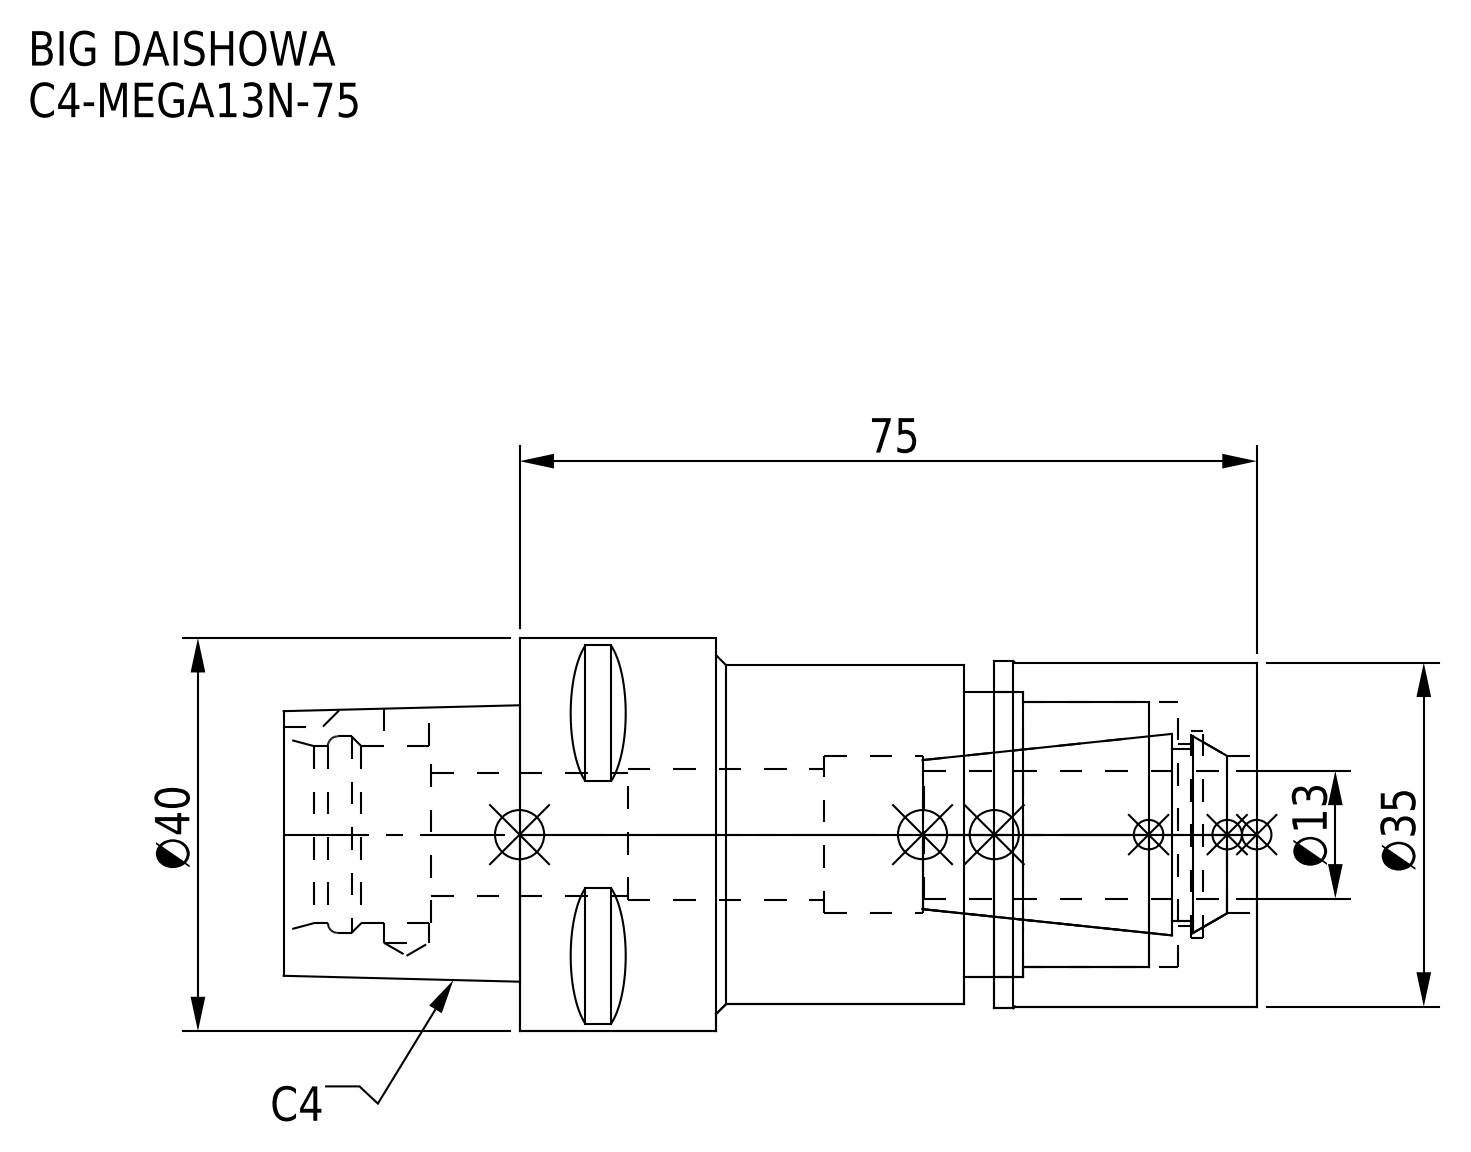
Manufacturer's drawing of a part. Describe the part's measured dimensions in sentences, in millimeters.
The part is named "C4-MEGA13N-75; MGN13_1.stp; C4-MEGA13N-75_1.stp; C4-MEGA13N-75-130_ASM.stp (+3 more)". Its 3-D file was written by "SolidWorks 2019 (CONFIG_CONTROL_DESIGN)". It is 2 solids with 95 faces: 38 planar, 39 cylindrical and 18 other. Overall it measures 99 by 40 by 40 millimeters. Its volume is 69 397 cubic millimeters and its surface area 22 108 square millimeters. Round holes: 1 of diameter 4.6, 1 of diameter 12.5, 1 of diameter 13.3, 1 of diameter 16, 1 of diameter 18, 1 of diameter 18.5, 1 of diameter 20, 1 of diameter 21, 1 of diameter 27, 1 of diameter 29. Round bosses or shafts: 1 of diameter 40, 1 of diameter 35.3, 1 of diameter 35, 1 of diameter 34.5. Partial cylindrical surfaces (rounded edges, fillets, slot ends): 1 of radius 3. The main face-to-face distances are 75, 44, 48.3, 11, 20, 26.7, 8, 18.7, 67, 15.7.
